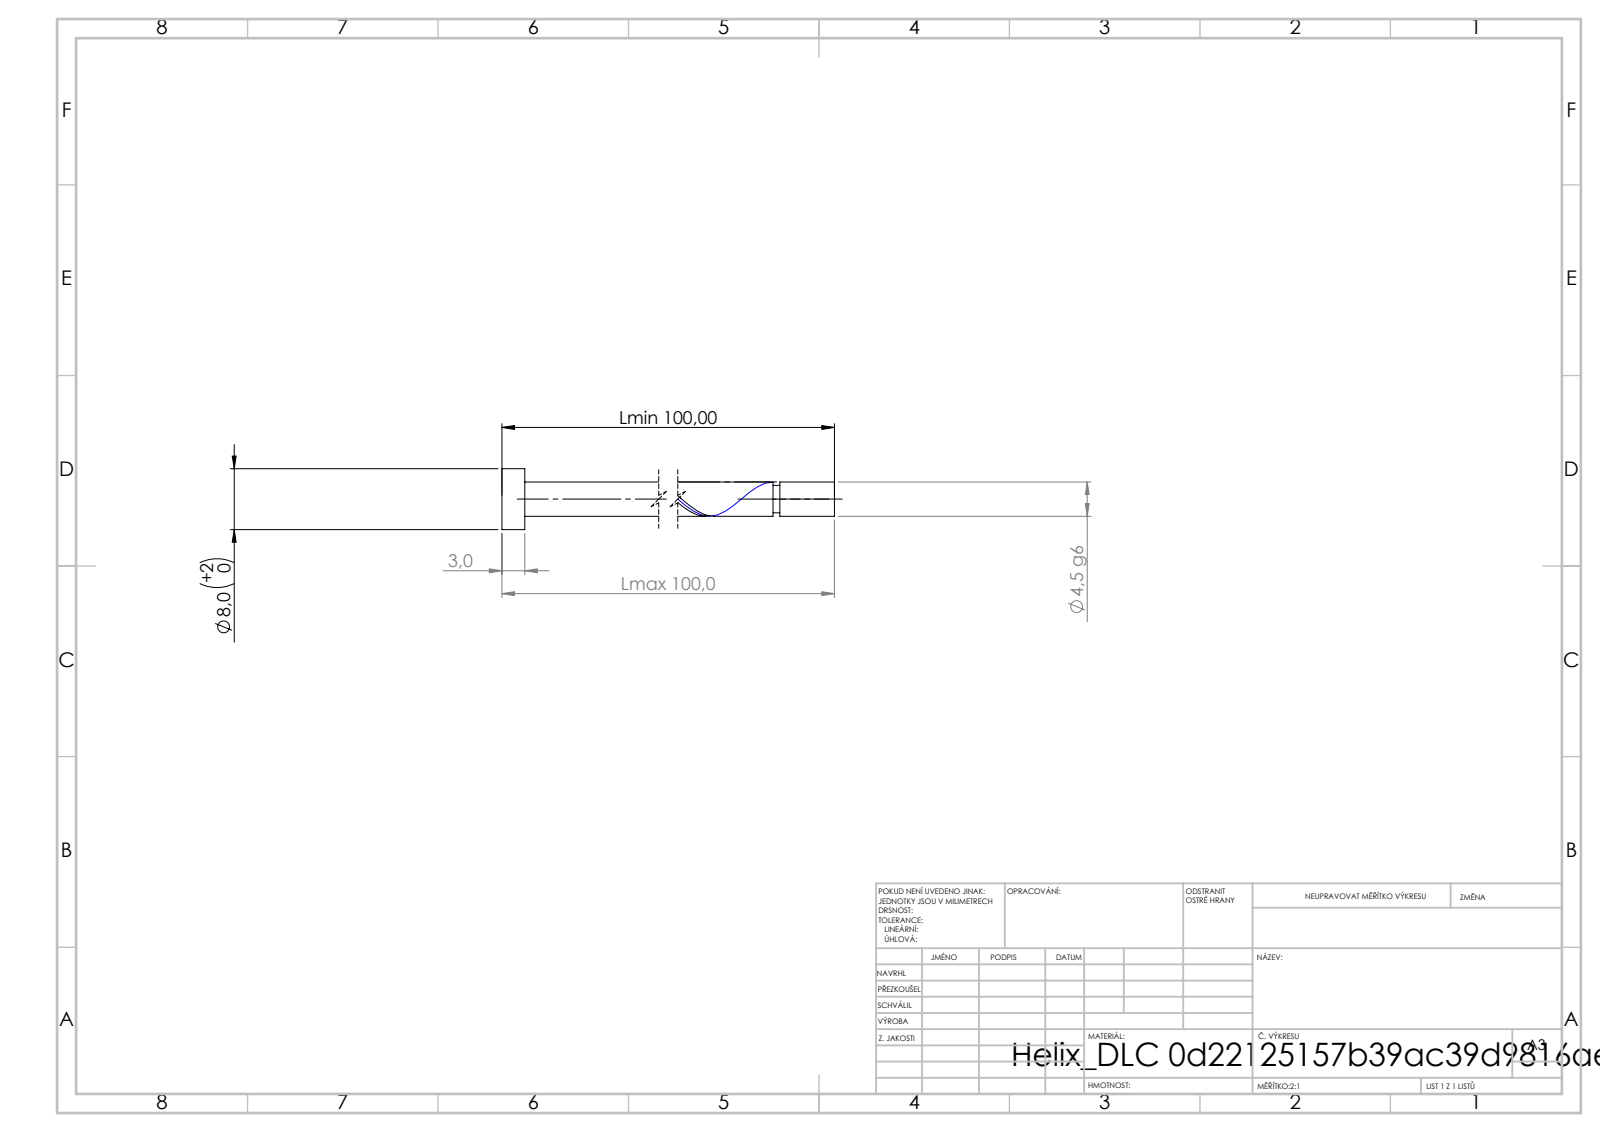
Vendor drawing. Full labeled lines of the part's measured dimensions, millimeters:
STEP written by: SolidWorks 2019 (CONFIG_CONTROL_DESIGN)
Units: millimetres
Bodies: 1 solid, 21 faces (6 planar, 14 cylindrical, 1 other)
Overall size (bounding box): 100 × 8 × 8
Volume: 1 673 mm³ · Surface area: 1 587 mm²
Round bosses / shafts (diameter × count): ⌀8 ×1, ⌀4.5 ×1, ⌀3.6 ×1
Main face-to-face distances: 3, 100, 97, 92.83, 89.83, 7.17, 91.93, 88.93, 0.9, 8.07
